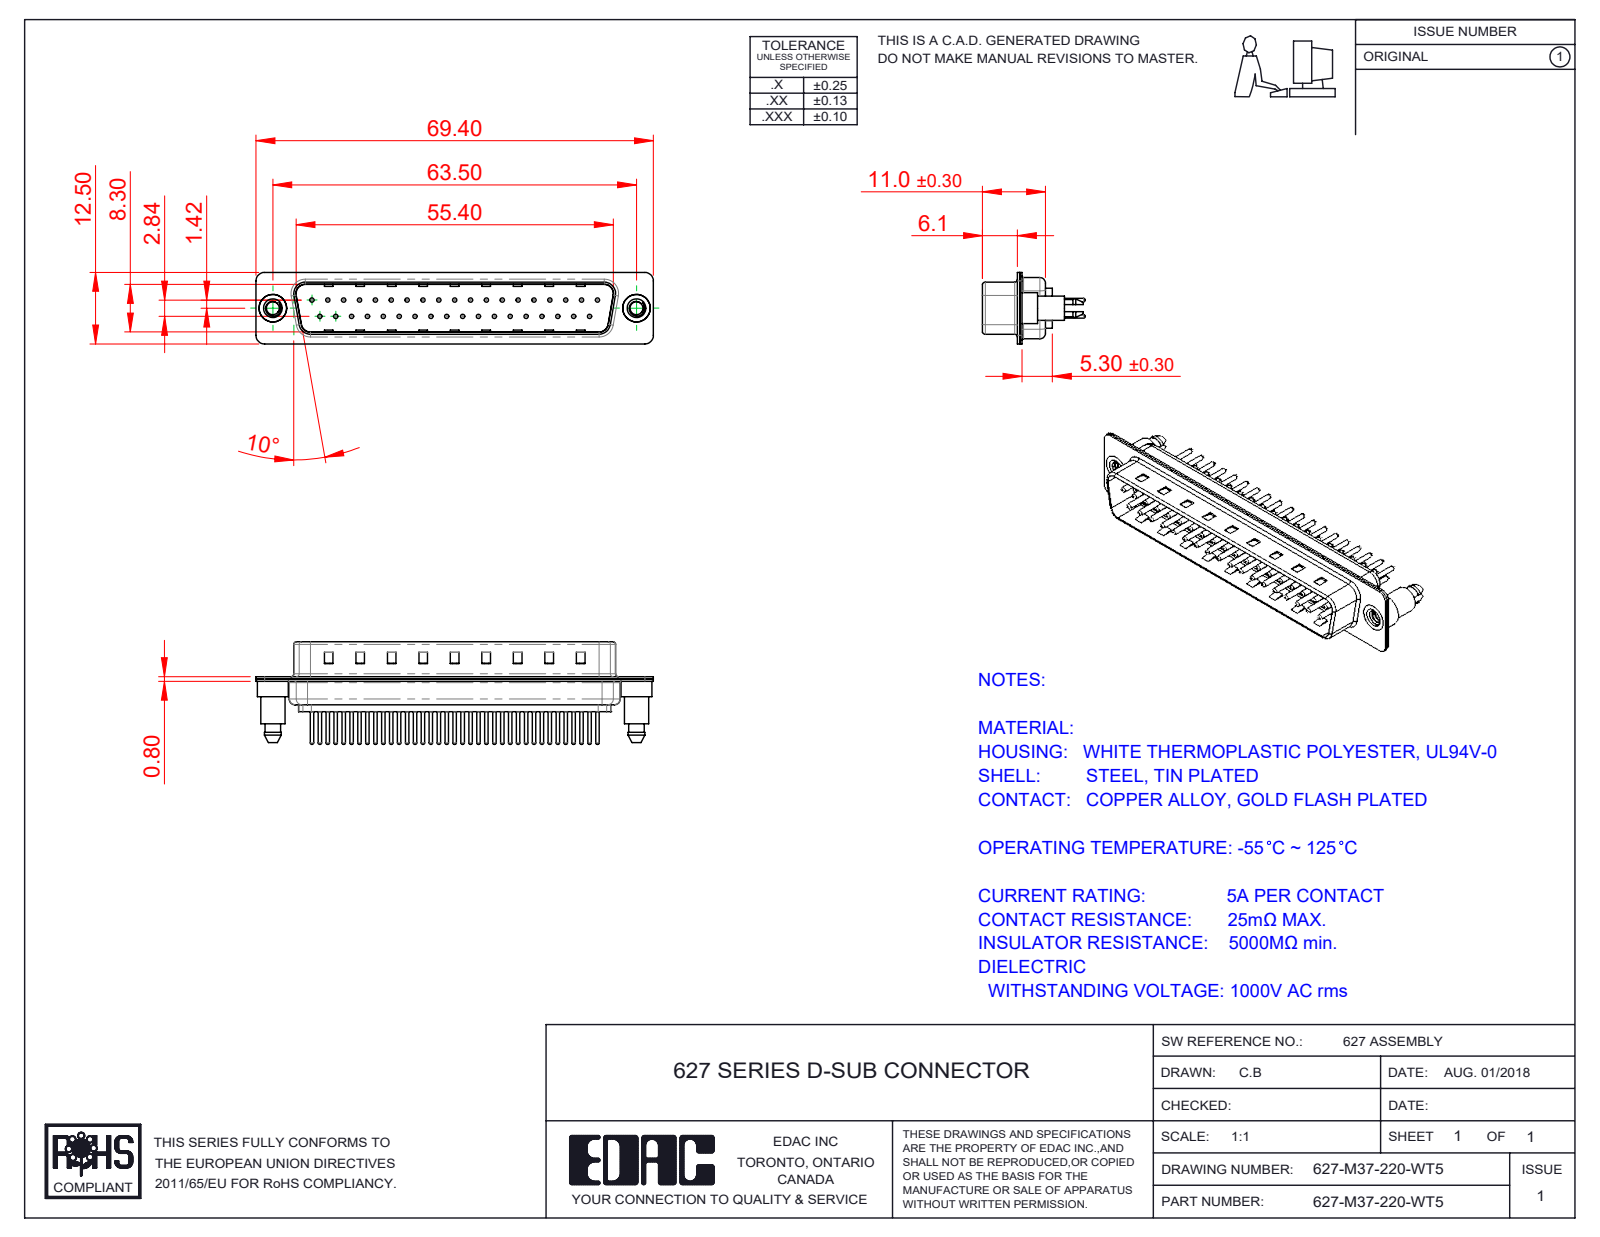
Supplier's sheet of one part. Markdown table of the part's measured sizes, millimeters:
| quantity | value |
| --- | --- |
| part name | 627M Shell Rear_37 Contacts; 627-M37-220-WT5; 627M Contact Row 1_20; 627M Contact Row 2_20 (+3 more) |
| STEP written by | SolidWorks 2020 (CONFIG_CONTROL_DESIGN) |
| units | millimeters |
| bodies | 42 solids, 1831 faces (478 planar, 691 cylindrical, 662 other) |
| overall size | 69.4 × 17.9 × 12.5 |
| volume | 3 902 mm³ |
| surface area | 9 603 mm² |
| round holes (diameter × count) | 0.75 × 37, 1.6 × 37, 2 × 37, 2.26 × 2, 4 × 2, 4.8 × 2 |
| round bosses / shafts (diameter × count) | 1.5 × 37, 0.6 × 37, 5.4 × 2, 4.9 × 2, 4.25 × 2 |
| partial cylindrical surfaces (radius × count) | 1.5 × 18, 2 × 12, 1.6 × 10, 0.5 × 8, 0.25 × 4, 0.6 × 4, 0.65 × 4, 0.9 × 4 |
| main face-to-face distances | 0.4, 0.8, 9.5, 9.1, 8.7, 9.9, 1.2, 5.7, 0.75, 0.35 |
| hole center spacings | 2.77, 5.54, 3.16, 8.31, 11.08, 13.85, 16.62, 19.39 |
